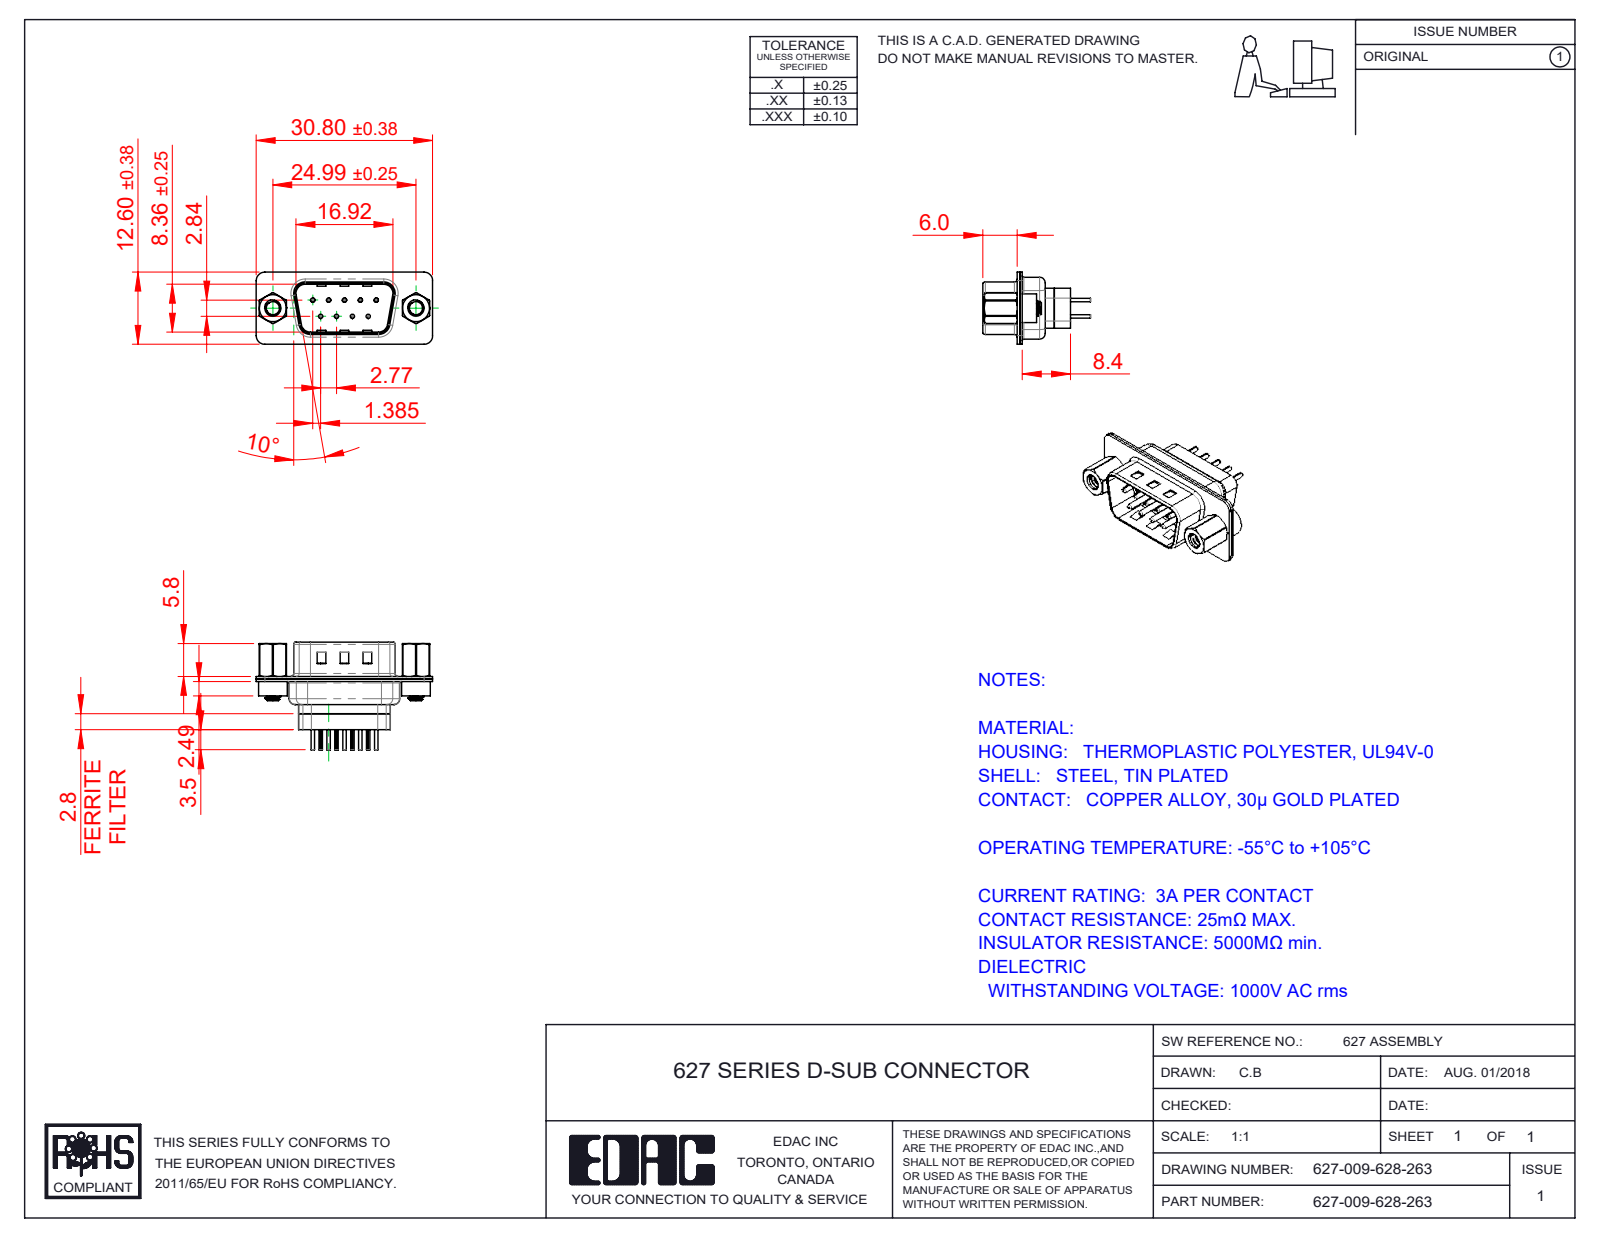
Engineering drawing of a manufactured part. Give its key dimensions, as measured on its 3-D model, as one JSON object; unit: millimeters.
{"part_name": "627 Contact Row 2_28L; 627 Contact Row 1_28L; 627 Housing_09 FF; 627 4-40 Hex Standoff (+4 more)", "step_written_by": "SolidWorks 2020 (CONFIG_CONTROL_DESIGN)", "units": "millimeters", "bodies": {"solids": 17, "faces": 1337, "planar": 351, "cylindrical": 555, "other": 431}, "overall_size": [30.8, 18.8, 12.6], "volume_mm3": 1767, "surface_area_mm2": 4864, "round_holes": [[0.2, 9], [0.35, 9], [1.1, 9], [1.6, 9], [2.26, 2], [2.29, 2], [4, 2], [4.8, 2]], "round_bosses_or_shafts": [[2, 9], [1.5, 9], [0.75, 9], [0.6, 9], [5, 2], [4.9, 2], [2.79, 2]], "partial_cylinders_radius": [[0.1, 18], [1.5, 18], [2, 12], [0.5, 8], [1.6, 8], [0.25, 4], [0.6, 4], [0.65, 4]], "face_to_face_distances": [0.4, 0.45, 0.9, 6.5, 6.05, 5.6, 0.82, 9.58, 8.4, 1.4], "hole_center_spacings": [3.16, 2.77, 5.54, 5.03, 5.04, 8.31, 7.48, 7.49]}
